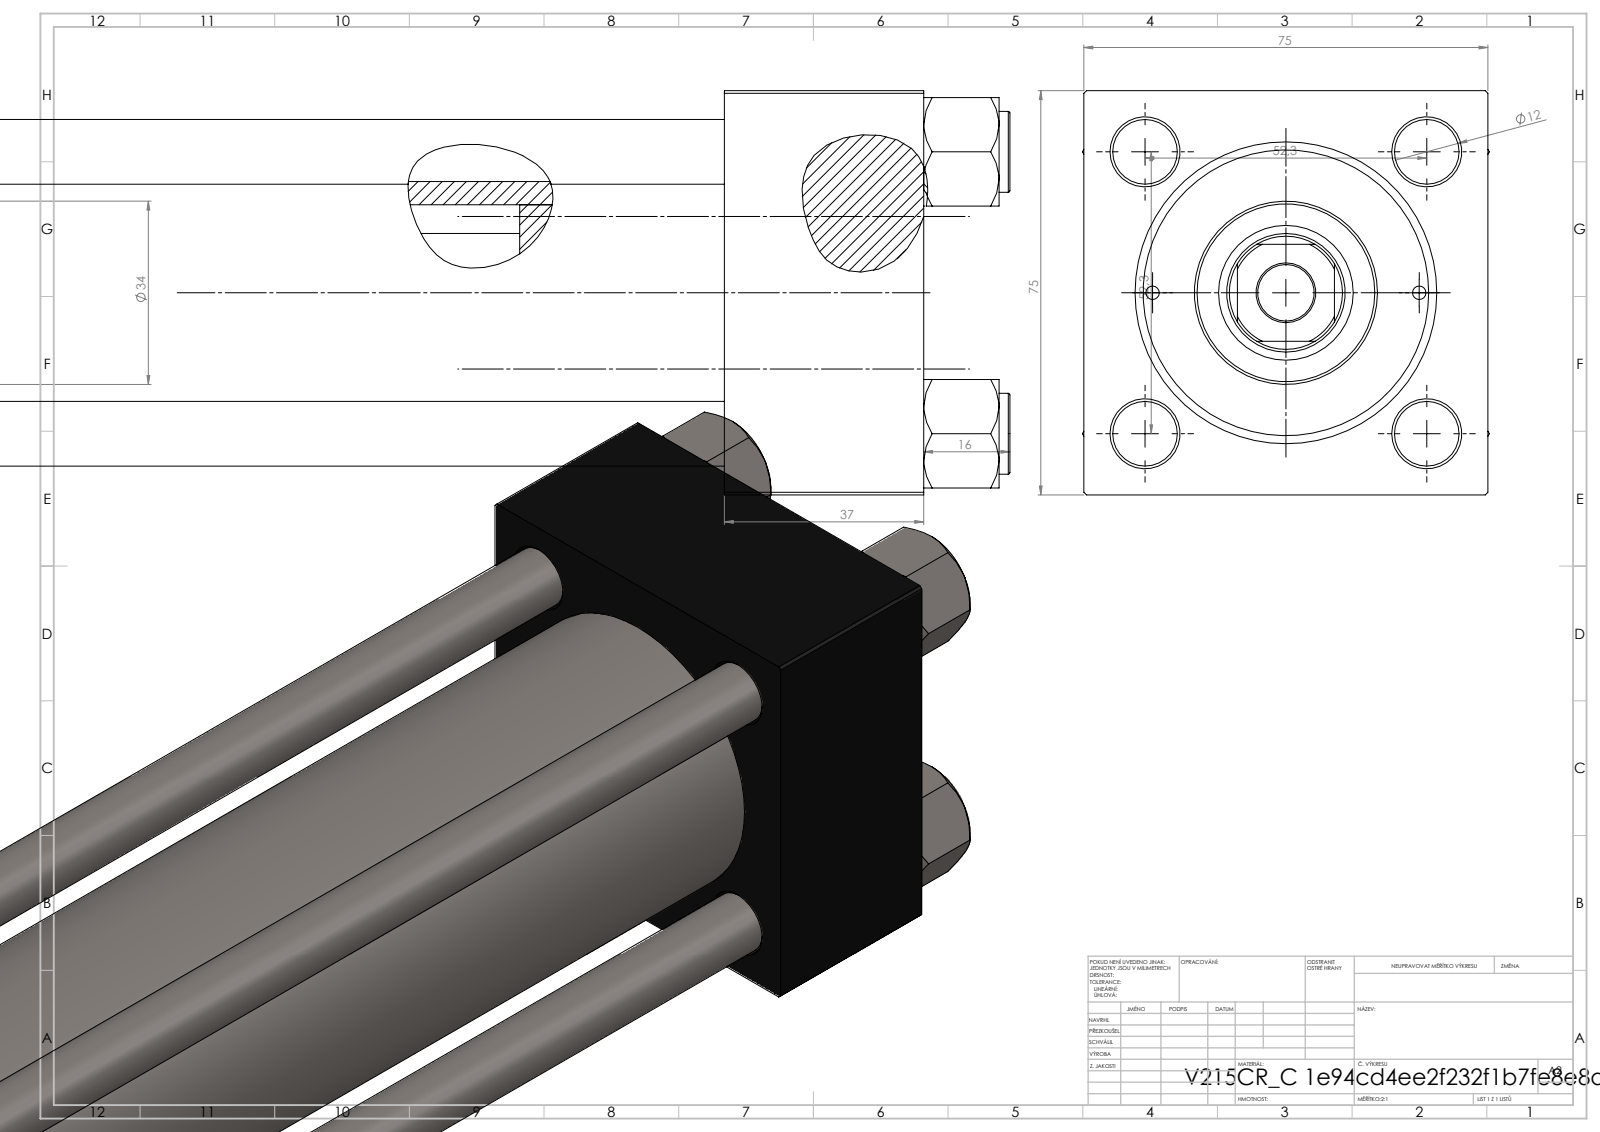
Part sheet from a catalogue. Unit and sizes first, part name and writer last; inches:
Units: inches
Overall size (bounding box): 16.732 × 2.974 × 2.953
Round holes (diameter × count): ⌀0.472 ×4, ⌀0.098 ×2, ⌀0.276 ×2, ⌀0.825 ×2, ⌀1.181 ×2, ⌀0.413 ×1, ⌀0.866 ×1, ⌀0.984 ×1, ⌀1.614 ×1, ⌀1.969 ×1, ⌀2.087 ×1
Round bosses / shafts (diameter × count): ⌀0.591 ×4, ⌀2.205 ×1, ⌀1.339 ×1
Partial cylindrical surfaces — rounded edges, fillets, slot ends (radius × count): R0.413 ×1
Main face-to-face distances: 2.953, 1.457, 15.118, 13.661, 12.795, 11.339, 2.323, 13.988, 12.531, 1.193
Hole centre spacings: 1.031, 1.456, 2.059, 2.253, 0.974, 2.912, 1.949, 12.736
Volume: 58.78 in³ · Surface area: 425.5 in²
Bodies: 11 solids, 1155 faces (528 planar, 91 cylindrical, 536 other)
Part name (STEP PRODUCT): V215CR_C_Body; V215CR_C_TYCINKA; V215_VC_A; V215CR_VCP_C (+1 more)
STEP written by: SolidWorks 2019 (CONFIG_CONTROL_DESIGN)
